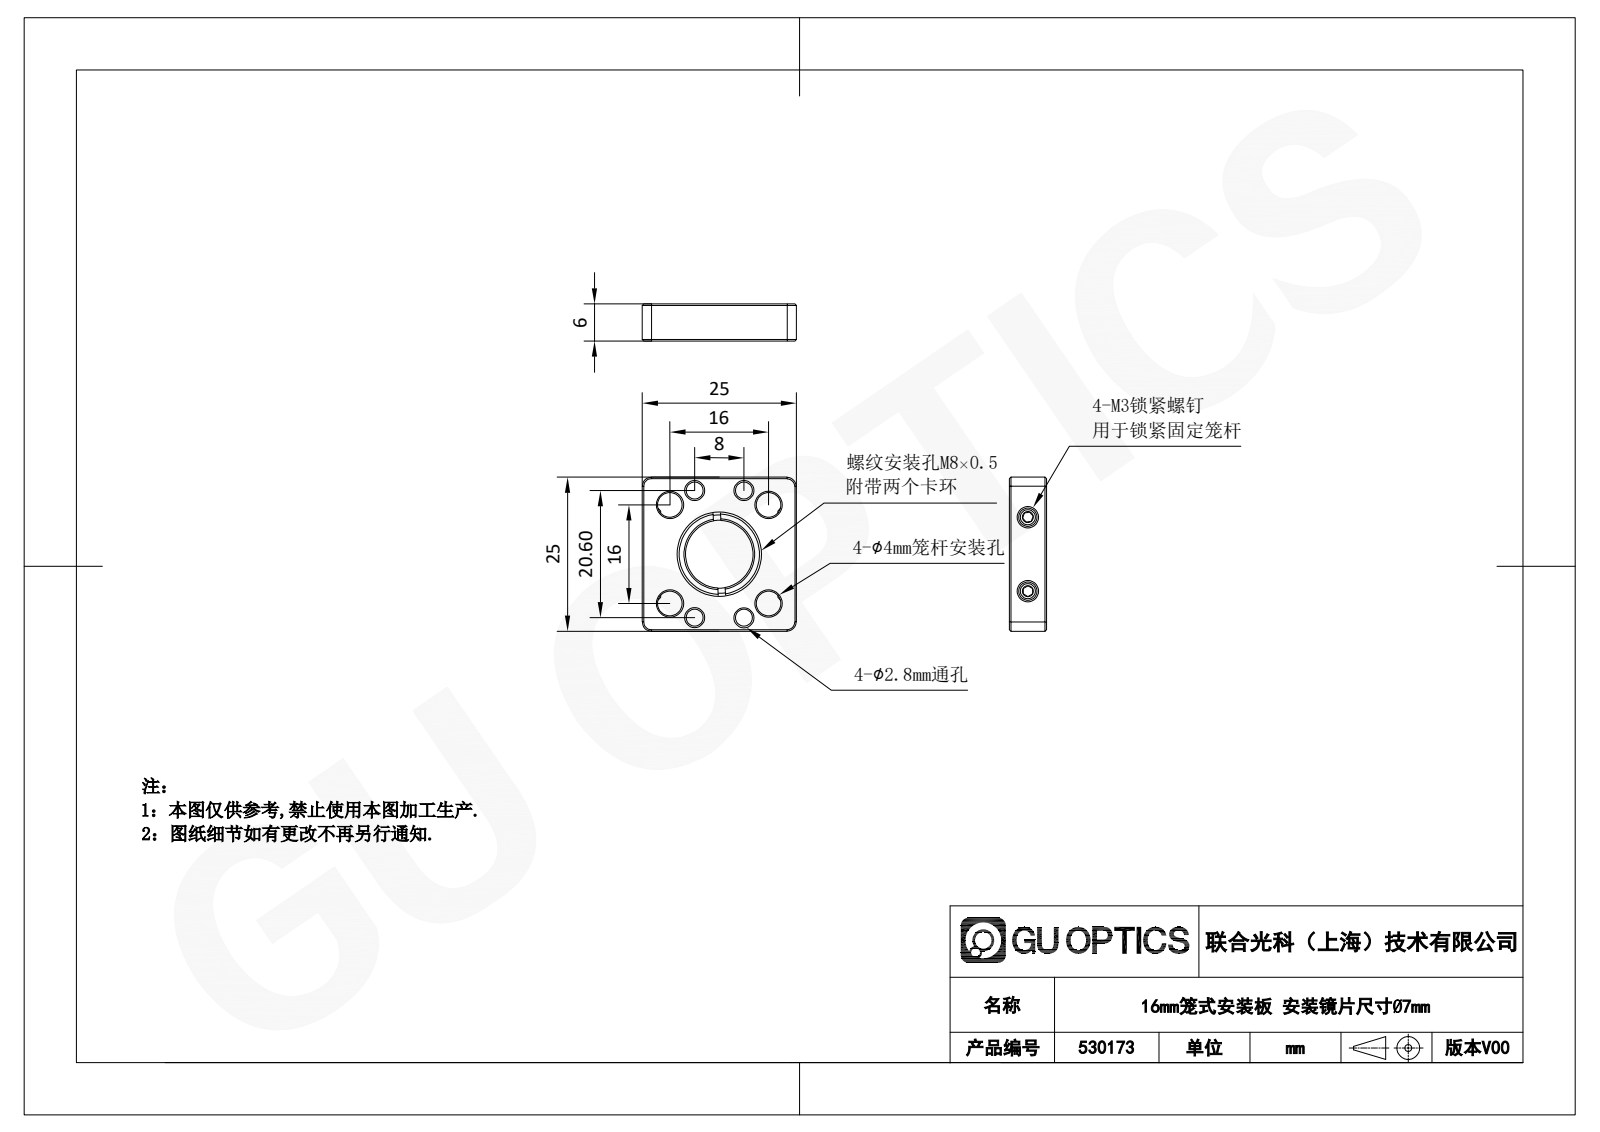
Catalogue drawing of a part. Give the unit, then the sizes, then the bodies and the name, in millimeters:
Units: millimetres
Overall size (bounding box): 25 × 25 × 6
Round holes (diameter × count): ⌀2.8 ×4, ⌀4 ×4, ⌀2.5 ×2, ⌀5.5 ×1, ⌀7.5 ×1
Round bosses / shafts (diameter × count): ⌀3 ×2, ⌀8 ×1
Partial cylindrical surfaces — rounded edges, fillets, slot ends (radius × count): R1.5 ×4
Main face-to-face distances: 6, 25, 2, 4, 21.56, 3, 22, 1.5, 1, 24
Hole centre spacings: 4.61, 11.05, 11.31, 12.22, 16, 18.73, 21.88, 8
Volume: 3 085 mm³ · Surface area: 2 687 mm²
Bodies: 7 solids, 280 faces (137 planar, 25 cylindrical, 118 other)
Part name (STEP PRODUCT): 530173
STEP written by: SolidWorks 2020 (CONFIG_CONTROL_DESIGN)
